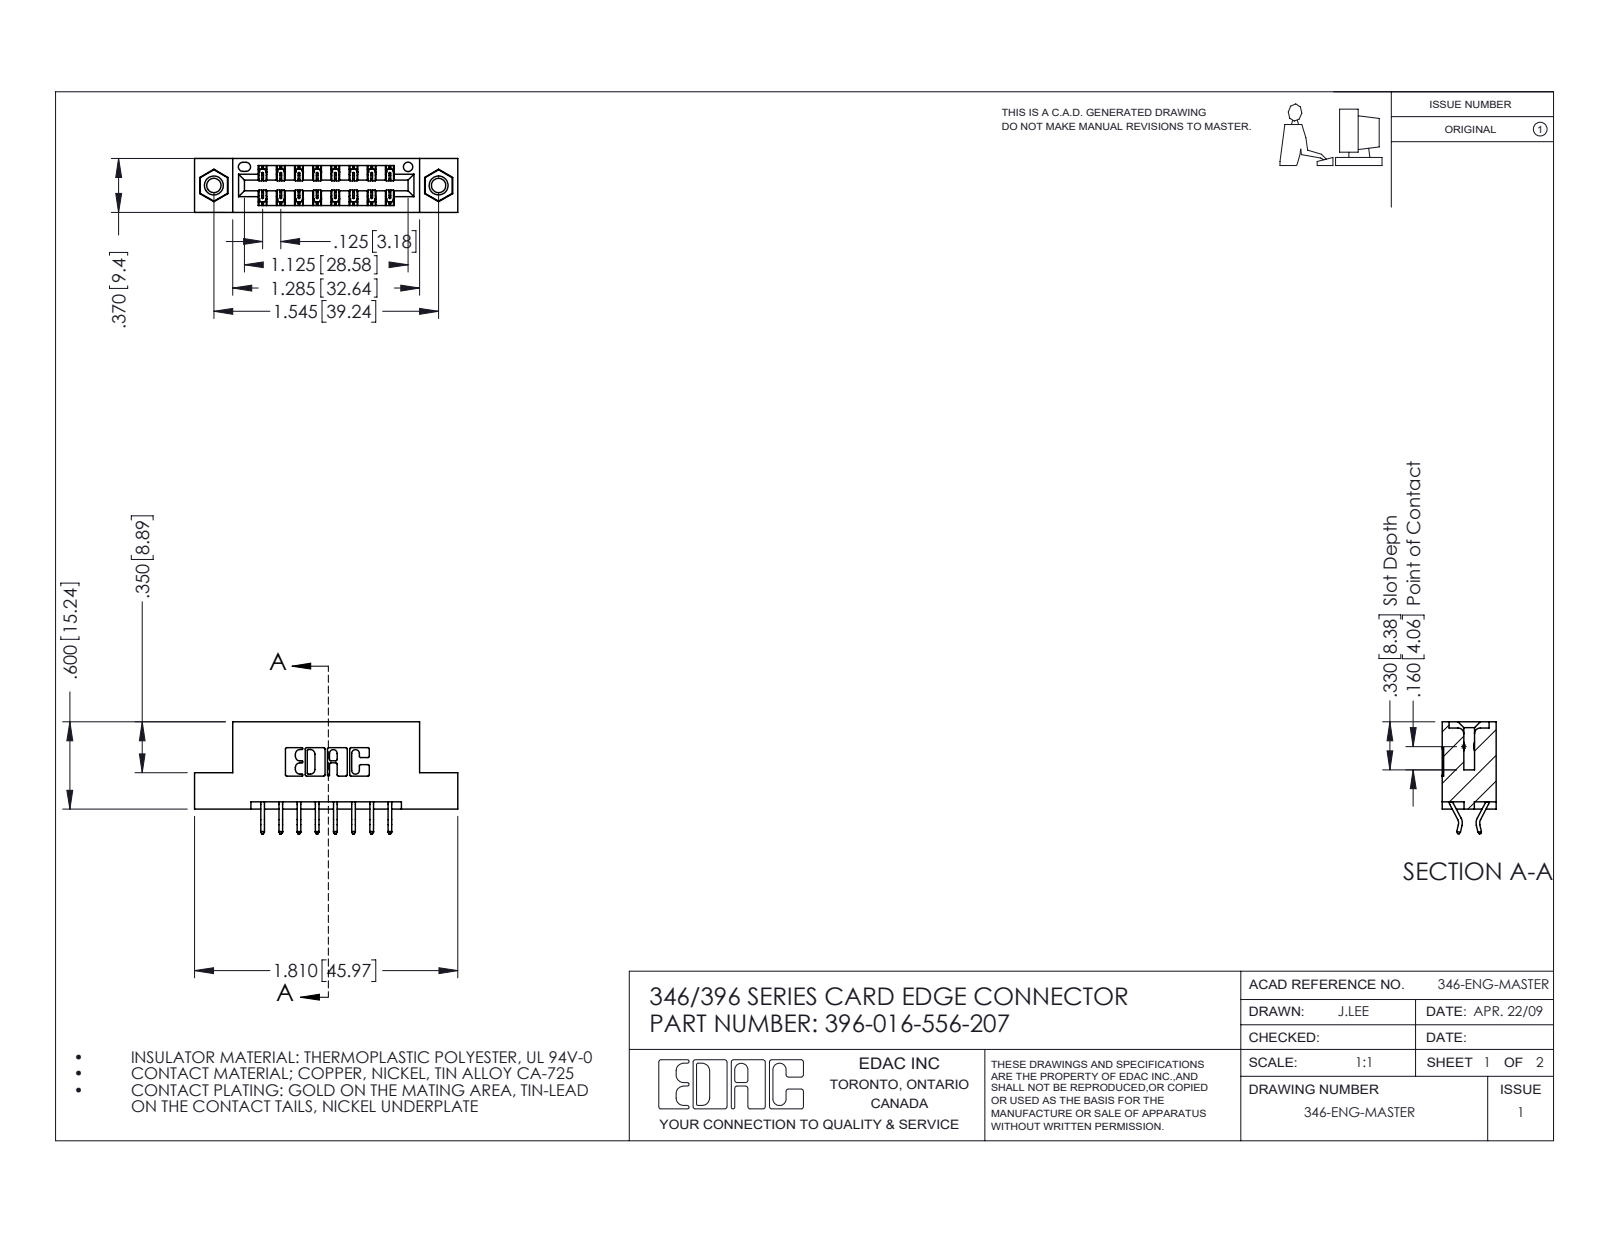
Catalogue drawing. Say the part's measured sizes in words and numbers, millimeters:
The part is named "346 Part_Flush Mounting Lugs - 0.156 Dia-TI; 345-250-001_345-250-005-103; 396-016-556-207; 345-292-001_556 Tail". Its 3-D file was written by "SolidWorks 2016 (CONFIG_CONTROL_DESIGN)". It is 19 solids with 1110 faces: 732 planar, 362 cylindrical and 16 other. Overall it measures 46 by 19.6 by 9.4 millimeters. Its volume is 4 210 cubic millimeters and its surface area 5 265 square millimeters. Round holes: 2 of diameter 2.5, 2 of diameter 3.2, 2 of diameter 4, 1 of diameter 1.6. Round bosses or shafts: 2 of diameter 3.9. Partial cylindrical surfaces (rounded edges, fillets, slot ends): 24 of radius 0.2, 22 of radius 0.3, 6 of radius 0.2, 6 of radius 0.8, 3 of radius 0.7, 2 of radius 0.3, 2 of radius 0.4, 2 of radius 0.6. The main face-to-face distances are 6.4, 9.4, 1.2, 8.2, 12.7, 0.6, 3.8, 5.6, 2.5, 4.4. The hole center spacings are 6.2, 34.1, 39.2.
